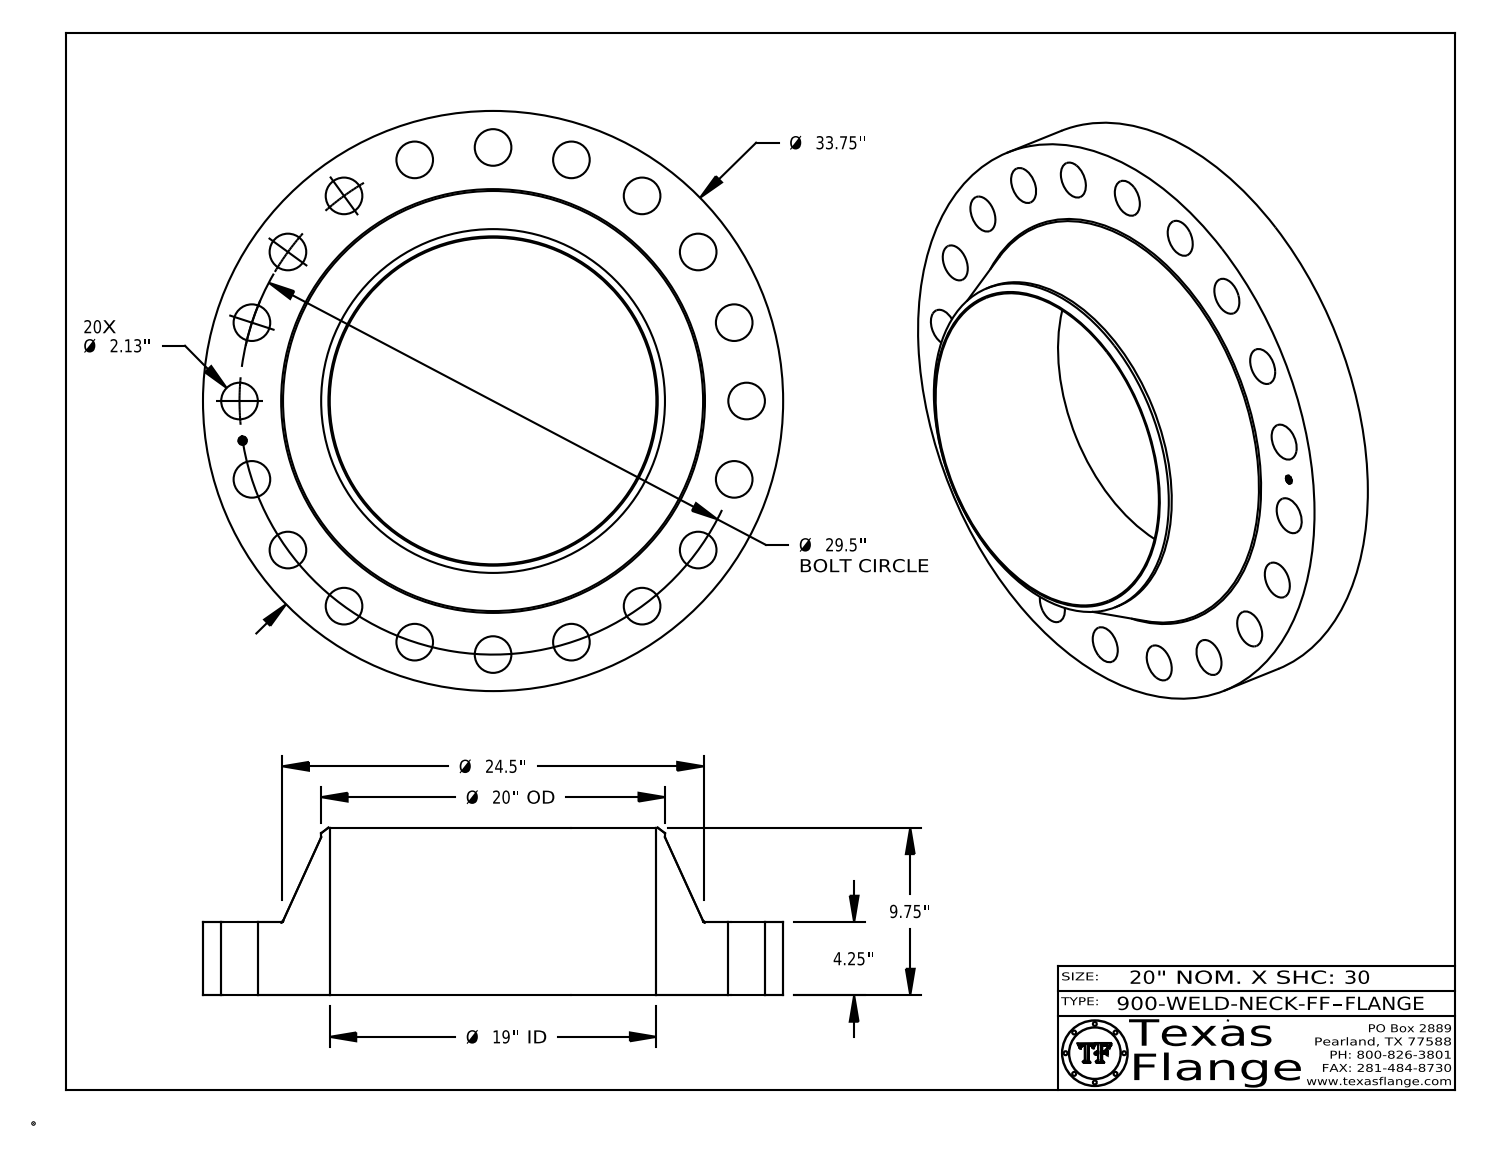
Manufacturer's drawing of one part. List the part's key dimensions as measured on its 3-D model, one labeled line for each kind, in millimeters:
Part name (STEP PRODUCT): 900-WELD-NECK-FF
STEP written by: CATIA V5 STEP AP214 (AUTOMOTIVE_DESIGN)
Units: millimetres
Bodies: 1 solid, 440 faces (368 planar, 66 cylindrical, 6 other)
Overall size (bounding box): 857.3 × 857.3 × 247.7
Volume: 46 440 000 mm³ · Surface area: 1 886 000 mm²
Round holes (diameter × count): ⌀54.1 ×20, ⌀12.6 ×1, ⌀482.6 ×1
Round bosses / shafts (diameter × count): ⌀0.8 ×8, ⌀857.3 ×1, ⌀508 ×1, ⌀9.9 ×1
Main face-to-face distances: 108, 247.7, 139.7, 107.6, 0.4, 140.1, 3.8, 3.7, 0.7, 2.4
Hole centre spacings: 374.7, 740.1, 117.2, 440.4, 529.8, 606.2, 667.6, 231.5
